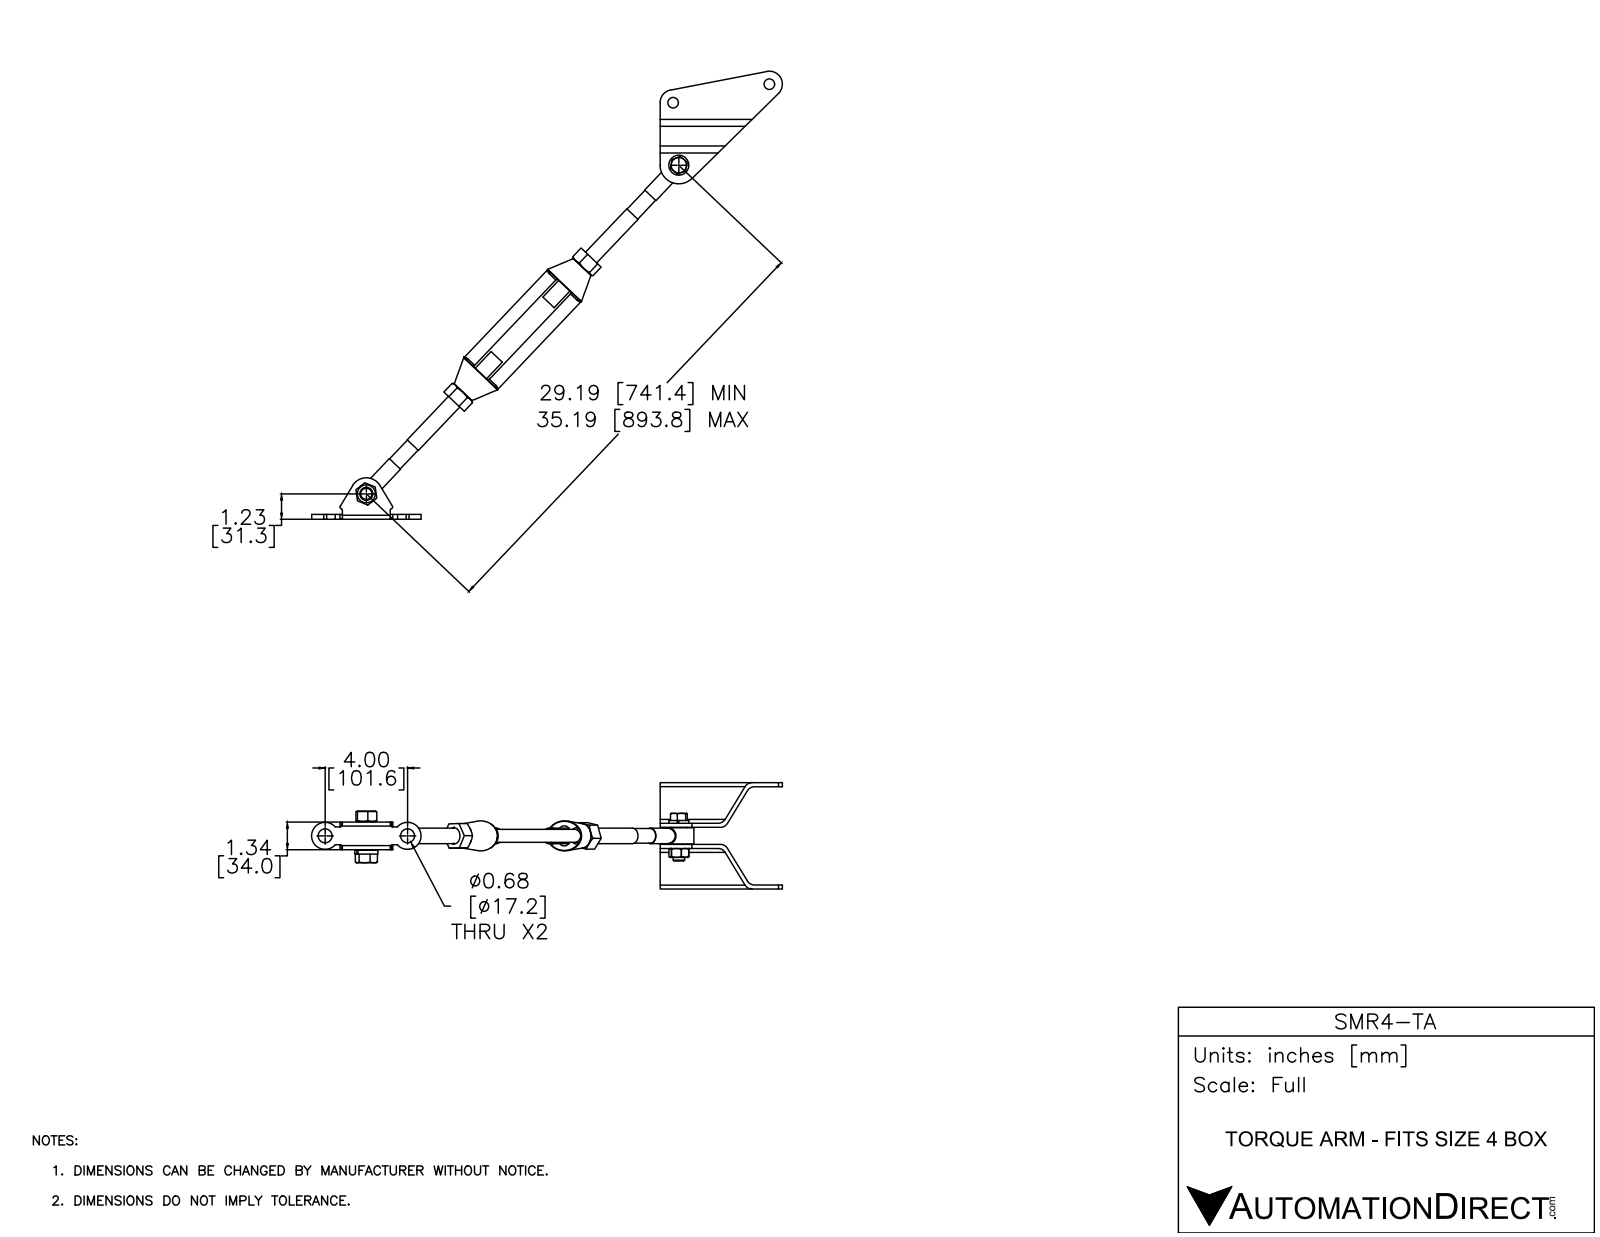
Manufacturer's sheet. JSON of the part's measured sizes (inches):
{"part_name": "SMR4-TARM; SMR4-TA_5; SMR4-TA_4; SMR4-TA_3 (+2 more)", "step_written_by": "SolidWorks 2017 (AUTOMOTIVE_DESIGN)", "units": "inches", "bodies": {"solids": 15, "faces": 327, "planar": 131, "cylindrical": 115, "other": 81}, "overall_size": [22.834, 21.727, 5.157], "volume_in3": 30.3, "surface_area_in2": 265.6, "round_holes": [[0.512, 2], [0.677, 2], [0.689, 2], [0.787, 2], [0.551, 1], [0.559, 1], [0.571, 1], [0.591, 1], [0.63, 1], [0.638, 1], [0.646, 1], [0.65, 1]], "round_bosses_or_shafts": [[0.75, 4], [1.457, 2], [0.711, 2], [0.63, 2], [1.114, 1], [0.965, 1], [0.878, 1], [0.787, 1]], "partial_cylinders_radius": [[0.394, 8], [0.079, 4], [0.118, 4], [0.197, 2], [0.63, 2], [0.654, 2], [0.5, 1], [0.778, 1]], "face_to_face_distances": [0.197, 4.961, 0.196, 1.969, 2.992, 0.02, 0.236, 5.157, 4.764, 0.827], "hole_center_spacings": [3.044, 4, 4.756, 5.897, 21.992, 24.107, 27.874]}
